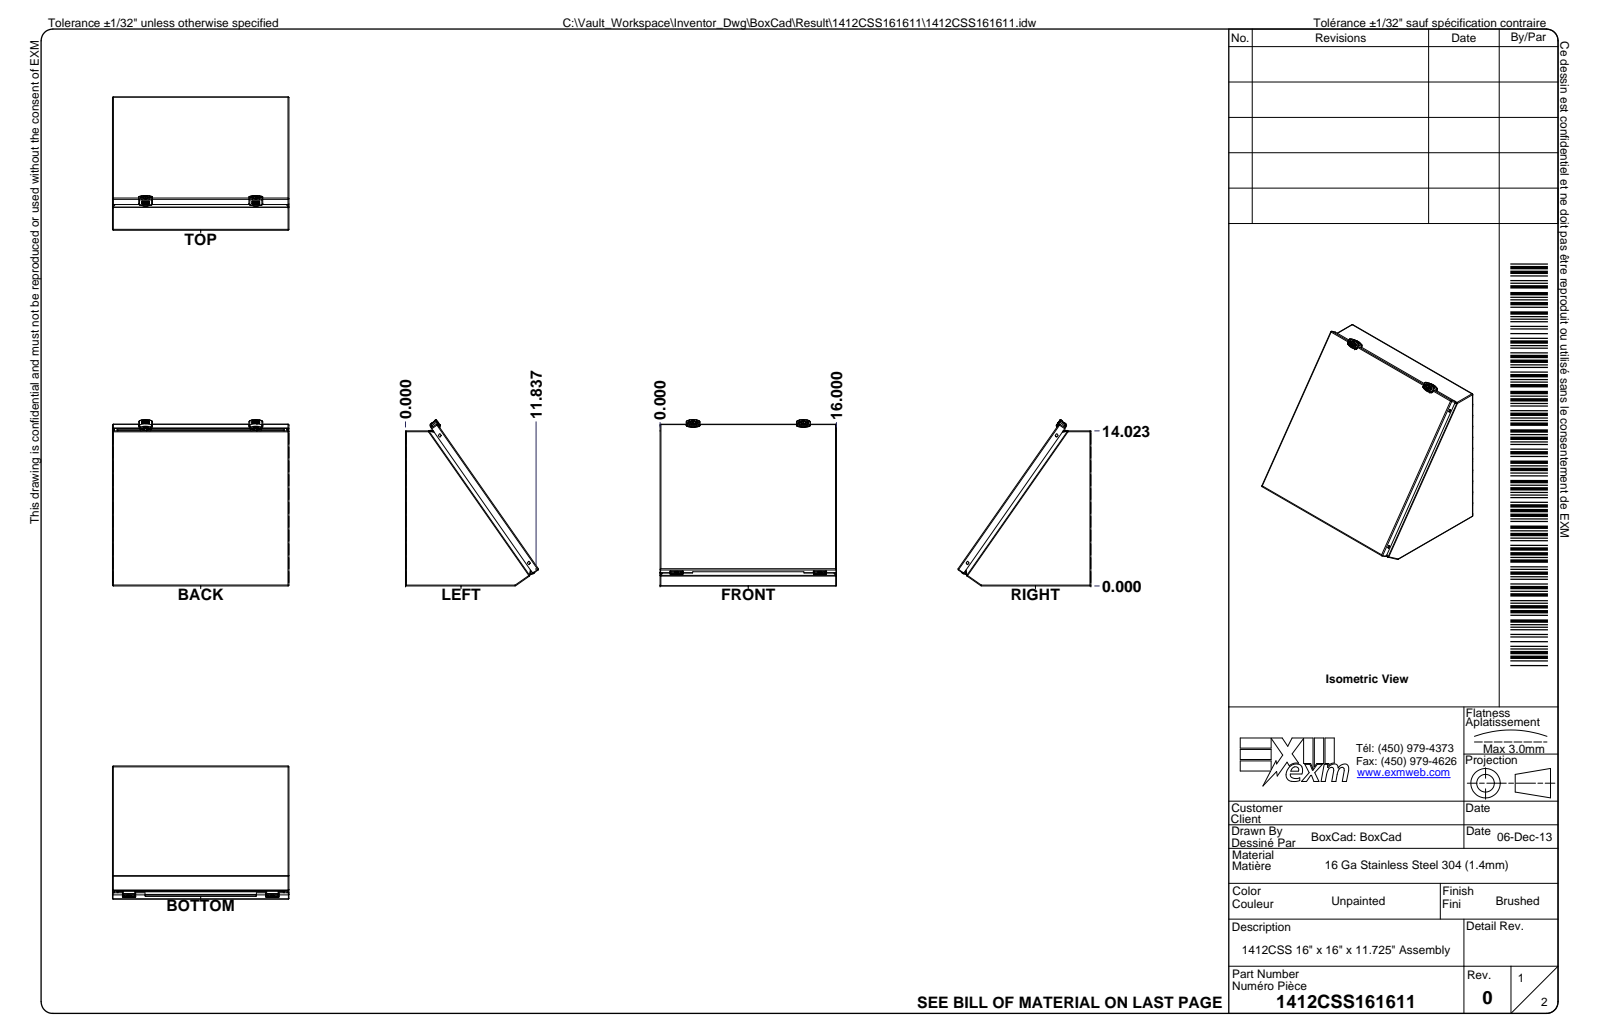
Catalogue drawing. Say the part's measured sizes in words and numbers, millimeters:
The part is named "1412CSS161611; 1412CSS161611B; 1412CSS161611B-P; STK-Q-08500 (+8 more)". Its 3-D file was written by "Autodesk Inventor 2024 (AUTOMOTIVE_DESIGN)". It is 59 solids with 8646 faces: 3985 planar, 2425 cylindrical and 2236 other. Overall it measures 406.4 by 381.2 by 306.2 millimeters. Its volume is 1 037 000 cubic millimeters and its surface area 1 410 000 square millimeters. Round holes: 10 of diameter 5.1, 6 of diameter 0.8, 5 of diameter 6.1, 4 of diameter 4.4, 4 of diameter 6, 4 of diameter 7.5, 2 of diameter 4.2, 2 of diameter 5.5, 2 of diameter 10.5, 2 of diameter 10.7, 1 of diameter 3.2, 1 of diameter 4.9. Round bosses or shafts: 5 of diameter 10, 5 of diameter 5.9, 5 of diameter 0.9, 4 of diameter 15, 4 of diameter 12, 4 of diameter 6, 3 of diameter 5, 2 of diameter 10.5. Partial cylindrical surfaces (rounded edges, fillets, slot ends): 238 of radius 0.2, 175 of radius 0.5, 88 of radius 1, 59 of radius 0.3, 42 of radius 0.1, 35 of radius 0.8, 28 of radius 2, 21 of radius 0.6. The main face-to-face distances are 1.4, 1.3, 405, 406.4, 403.6, 1.4, 356.2, 354.8, 354.8, 353.4. The hole center spacings are 350.7, 330.2, 26.8, 257.3, 15, 41.8, 215.5, 230.5.
